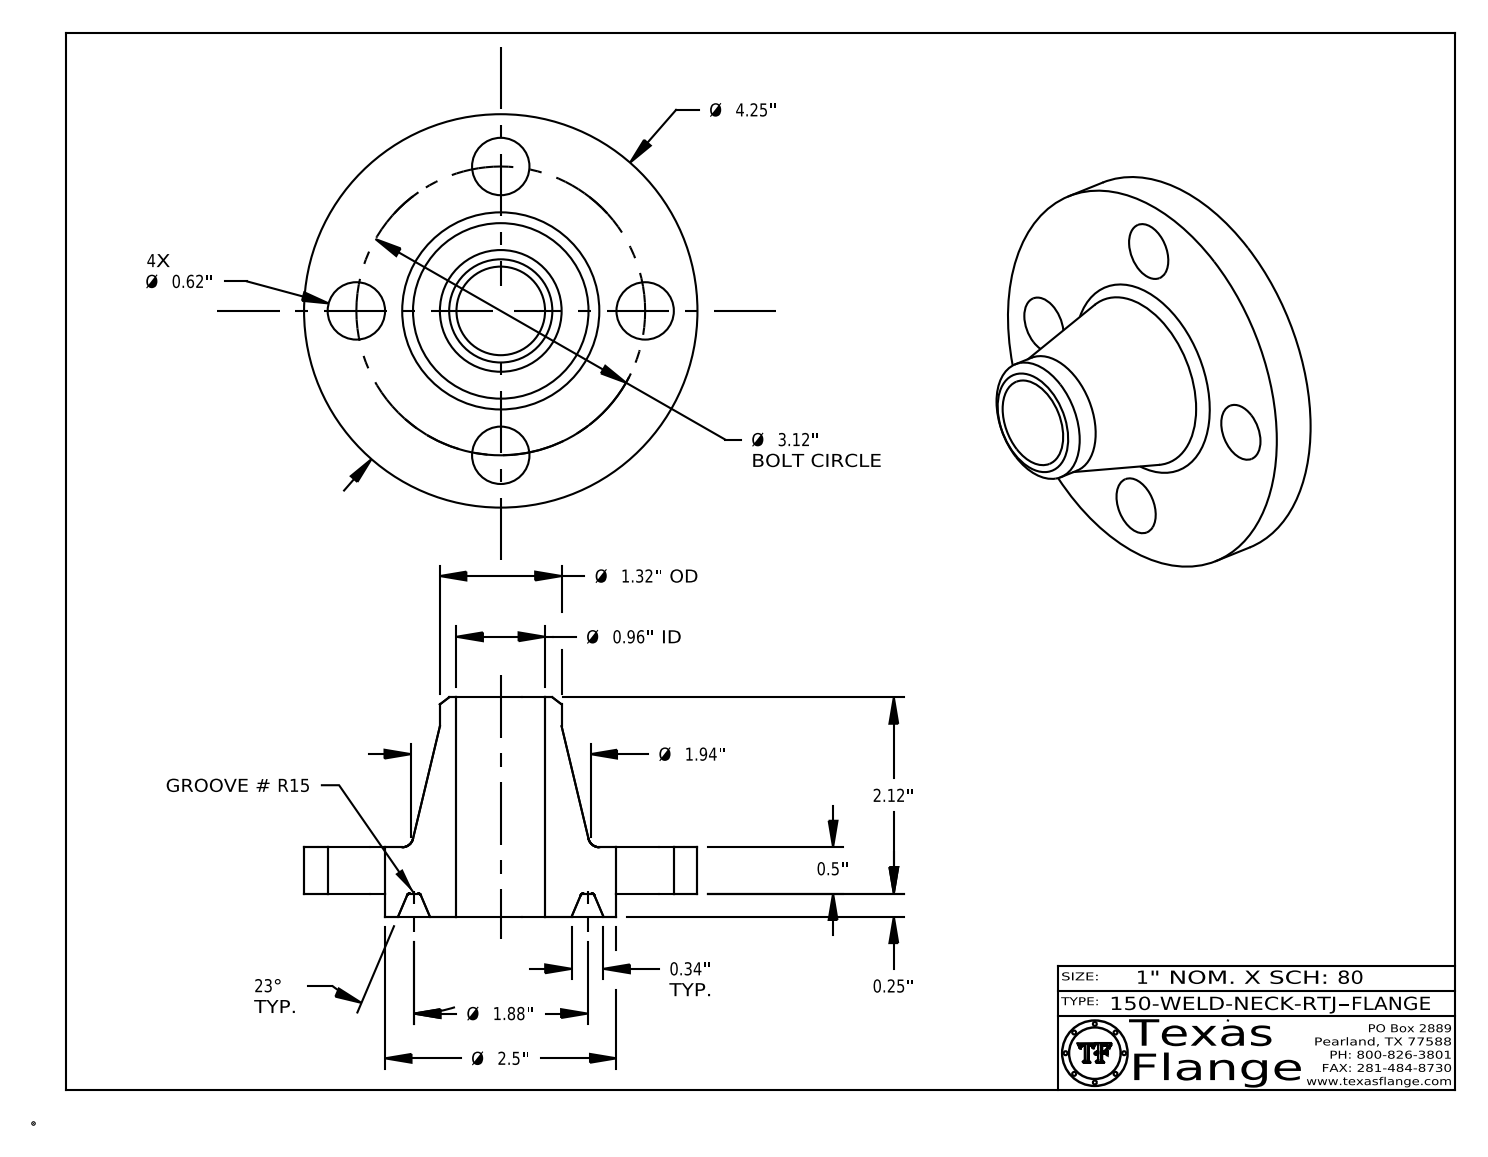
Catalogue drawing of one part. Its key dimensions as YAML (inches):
part_name: "150-WELD-NECK-RTJ"
step_written_by: "CATIA V5 STEP AP214 (AUTOMOTIVE_DESIGN)"
units: inches
bodies: {solids: 1, faces: 421, planar: 371, cylindrical: 36, other: 14}
overall_size: [4.25, 4.25, 2.37]
volume: 8.835
surface_area: 52.28
round_holes:
  - {diameter: 0.62, count: 4}
  - {diameter: 0.495, count: 1}
  - {diameter: 0.957, count: 1}
round_bosses_or_shafts:
  - {diameter: 0.03, count: 8}
  - {diameter: 4.25, count: 1}
  - {diameter: 2.5, count: 1}
  - {diameter: 1.315, count: 1}
  - {diameter: 0.39, count: 1}
face_to_face_distances: [0.5, 0.25, 0.75, 2.37, 2.12, 1.62, 0.745, 0.495, 1.625, 0.148]
hole_center_spacings: [1.56, 2.206, 1.194, 2.882, 3.12, 1.56]
